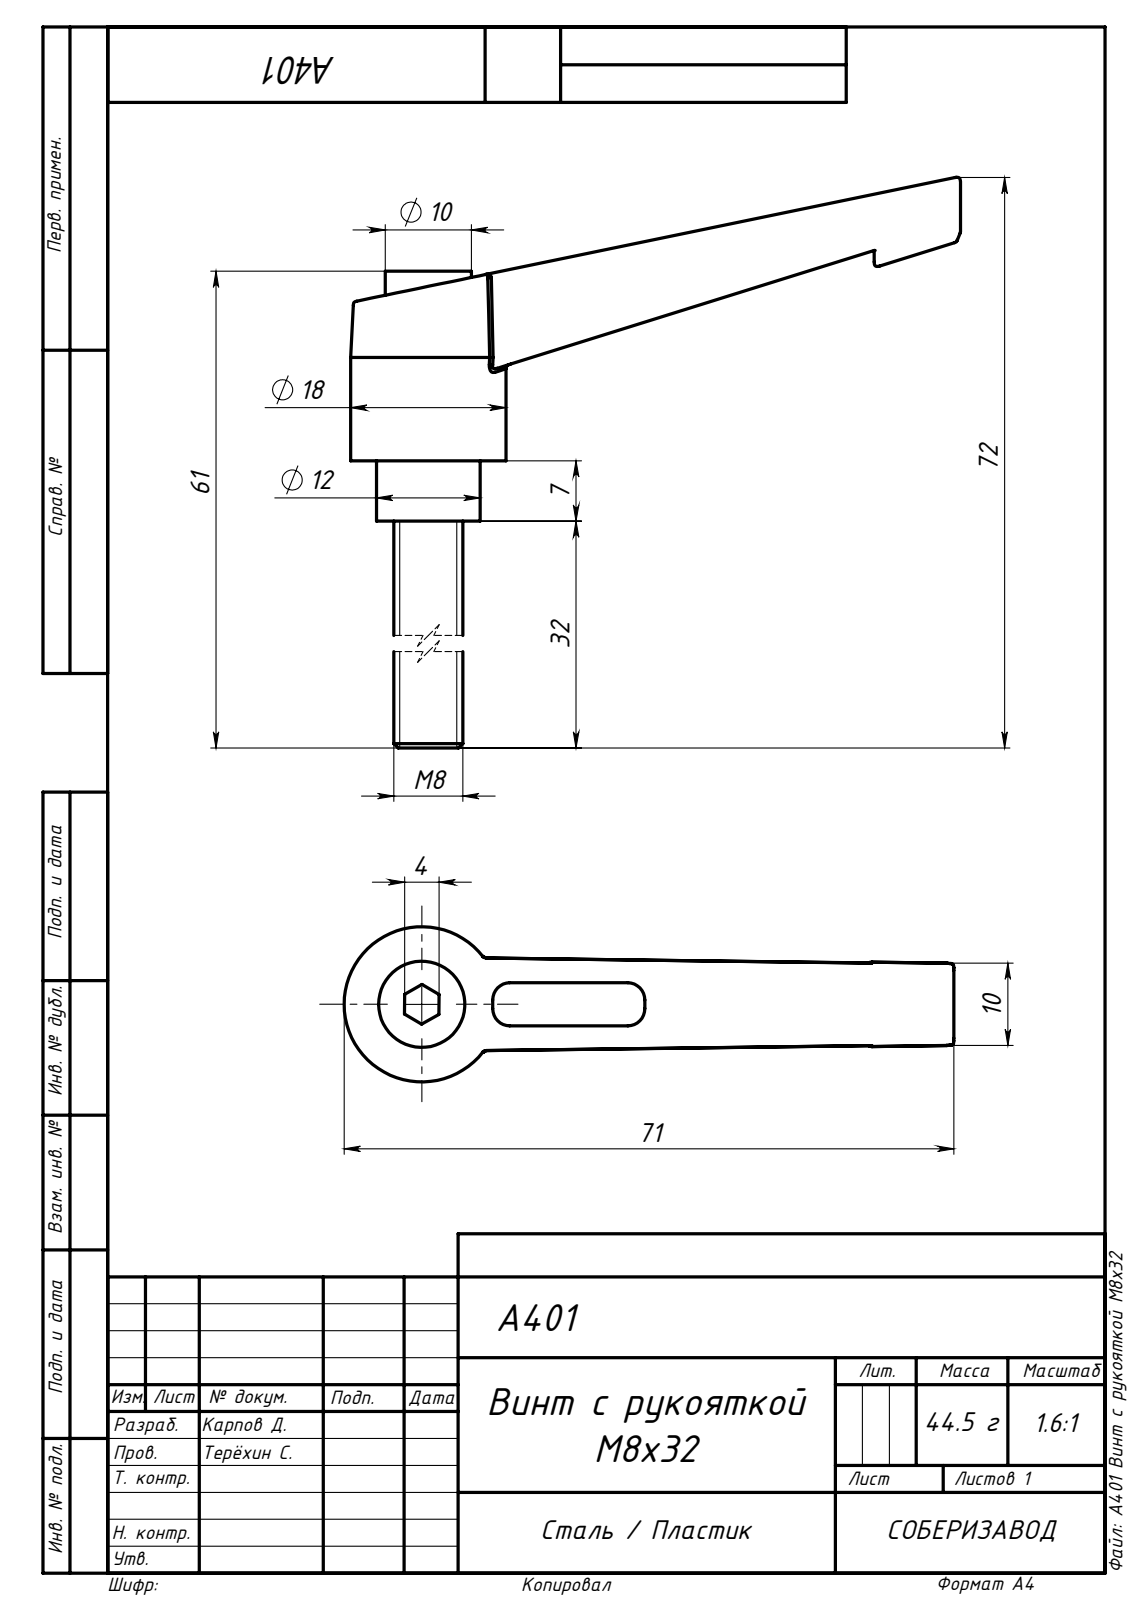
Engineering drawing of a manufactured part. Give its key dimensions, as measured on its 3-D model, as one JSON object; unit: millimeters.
{"part_name": "A401 Винт с рукояткой М8х32", "step_written_by": "SolidWorks 2020 (AUTOMOTIVE_DESIGN)", "units": "millimeters", "bodies": {"solids": 1, "faces": 81, "planar": 29, "cylindrical": 12, "other": 40}, "overall_size": [71.9, 70.69, 18], "volume_mm3": 9986, "surface_area_mm2": 5259, "round_bosses_or_shafts": [[18, 1], [12, 1], [10, 1], [8, 1]], "partial_cylinders_radius": [[2, 4]], "face_to_face_distances": [6.9, 22, 7, 29, 44.11, 32, 39, 61, 4, 58]}
